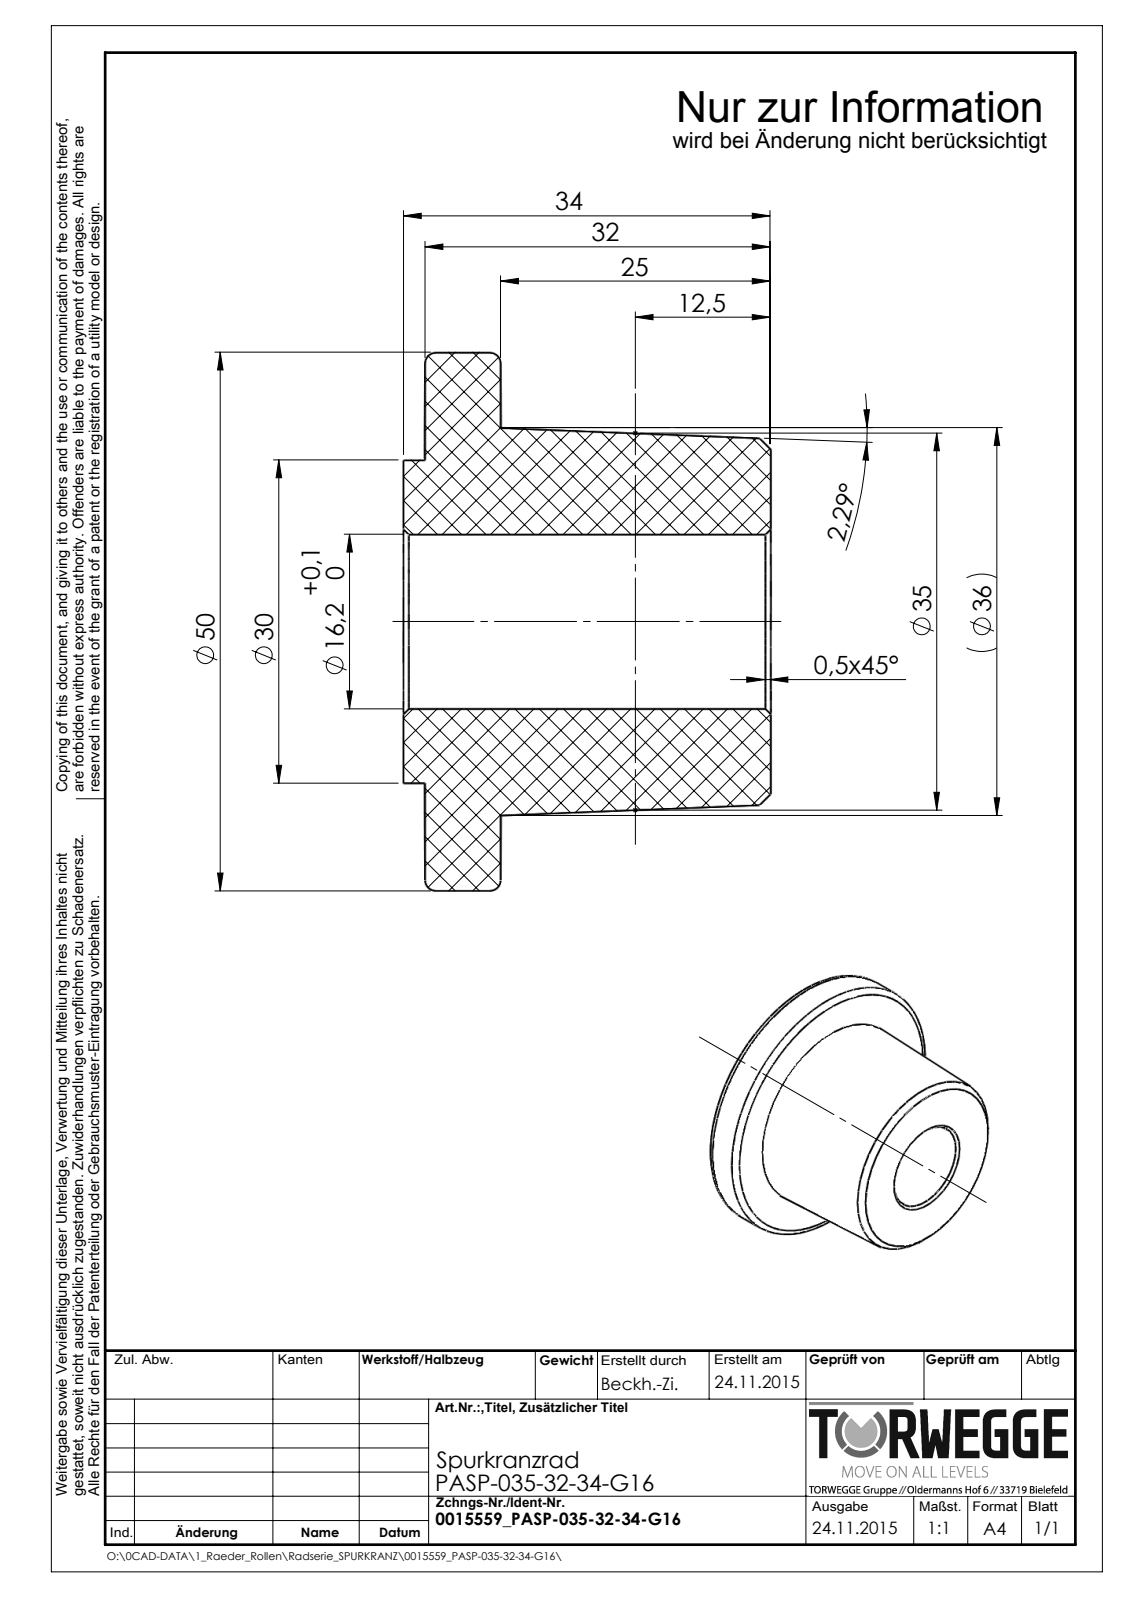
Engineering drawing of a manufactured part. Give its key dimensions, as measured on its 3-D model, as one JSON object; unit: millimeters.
{"part_name": "0015559_PASP-035-32-34-G16", "step_written_by": "SolidWorks 2014 (AUTOMOTIVE_DESIGN)", "units": "millimeters", "bodies": {"solids": 1, "faces": 22, "planar": 4, "cylindrical": 6, "other": 12}, "overall_size": [50, 50, 34], "volume_mm3": 32075, "surface_area_mm2": 8947, "round_holes": [[16.2, 1]], "round_bosses_or_shafts": [[50, 1], [30, 1]], "face_to_face_distances": [7, 32, 25, 2, 9, 34]}
